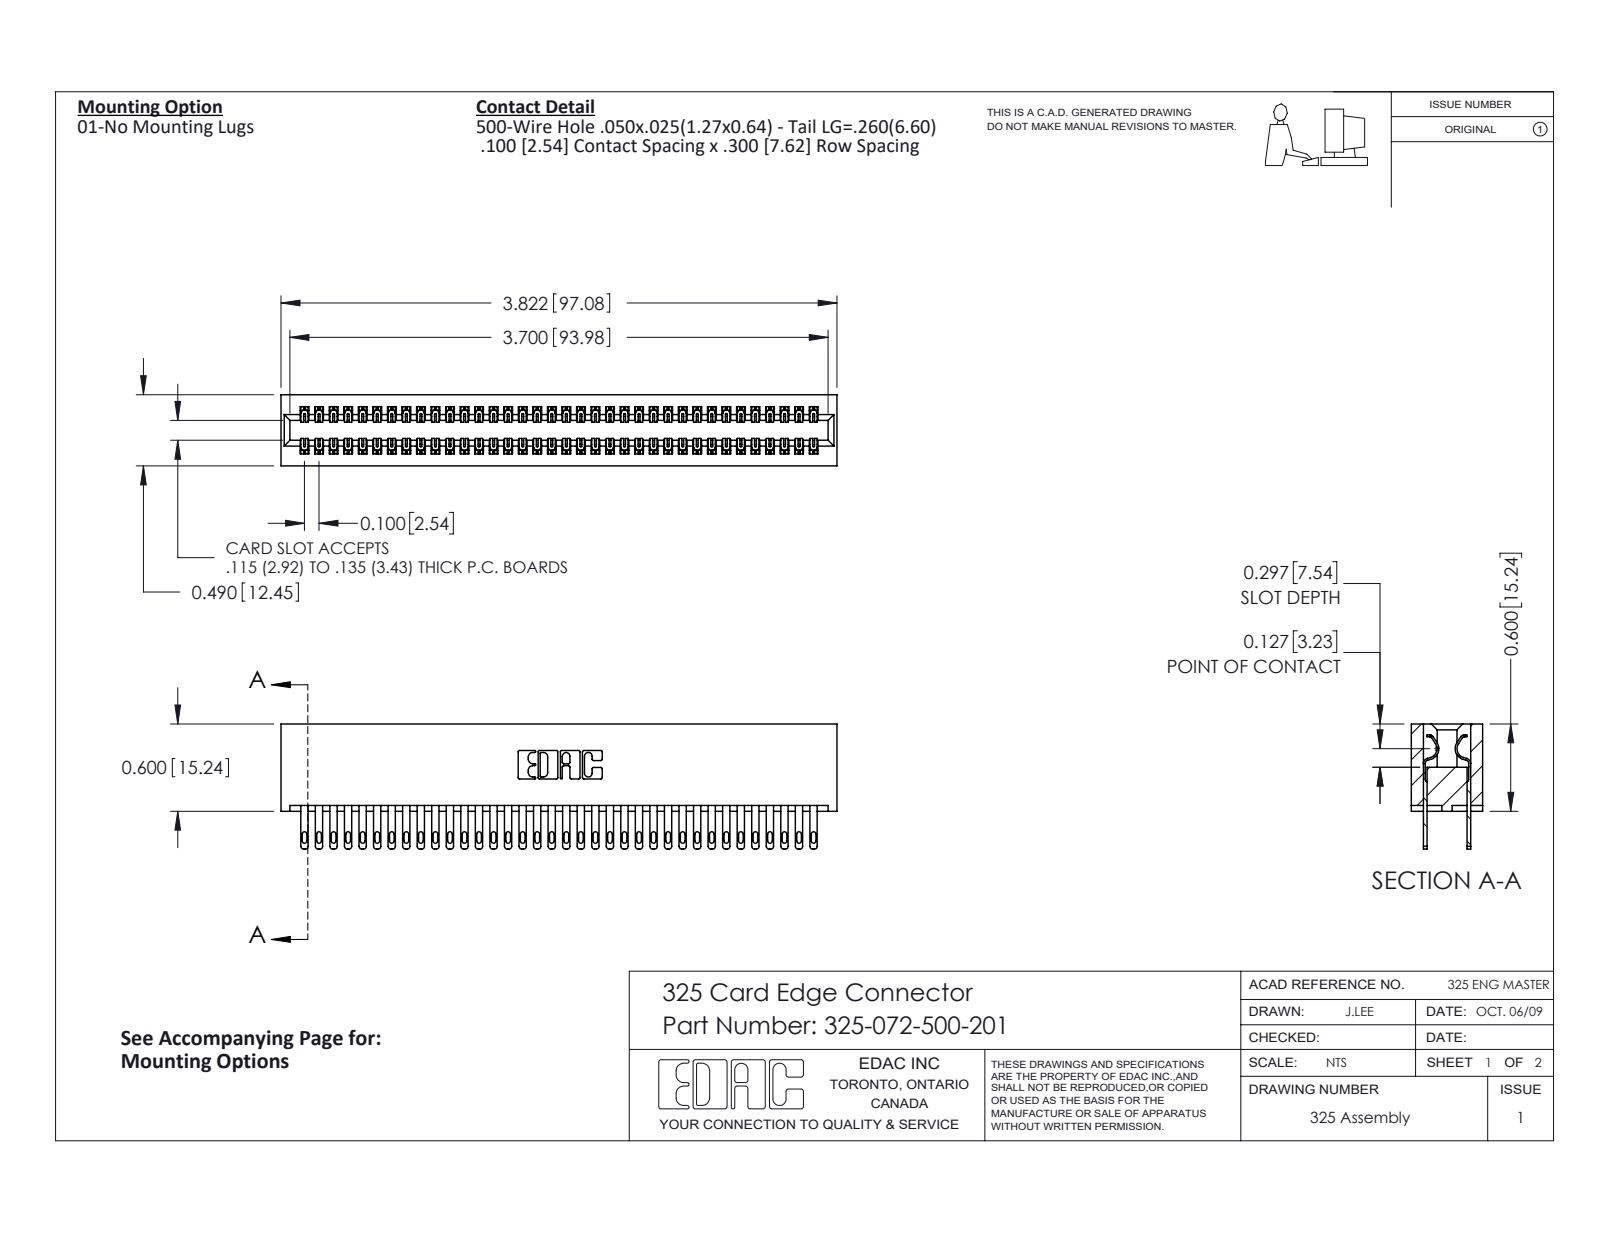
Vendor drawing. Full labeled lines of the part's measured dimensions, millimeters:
Part name (STEP PRODUCT): 325-292-001_325-293-100; 325 Part_Lugless; 325-072-500-201
STEP written by: SolidWorks 2016 (CONFIG_CONTROL_DESIGN)
Units: millimetres
Bodies: 73 solids, 3562 faces (2226 planar, 1336 cylindrical, 0 other)
Overall size (bounding box): 97.1 × 21.8 × 12.4
Volume: 13 300 mm³ · Surface area: 17 370 mm²
Partial cylindrical surfaces — rounded edges, fillets, slot ends (radius × count): R0.2 ×108, R0.4 ×72, R0.5 ×72, R0.3 ×22, R0.2 ×6, R0.8 ×6, R0.7 ×3, R0.4 ×2
Main face-to-face distances: 2.1, 10.3, 7.6, 2.7, 9.7, 0.6, 8.3, 12.4, 7, 14.2
